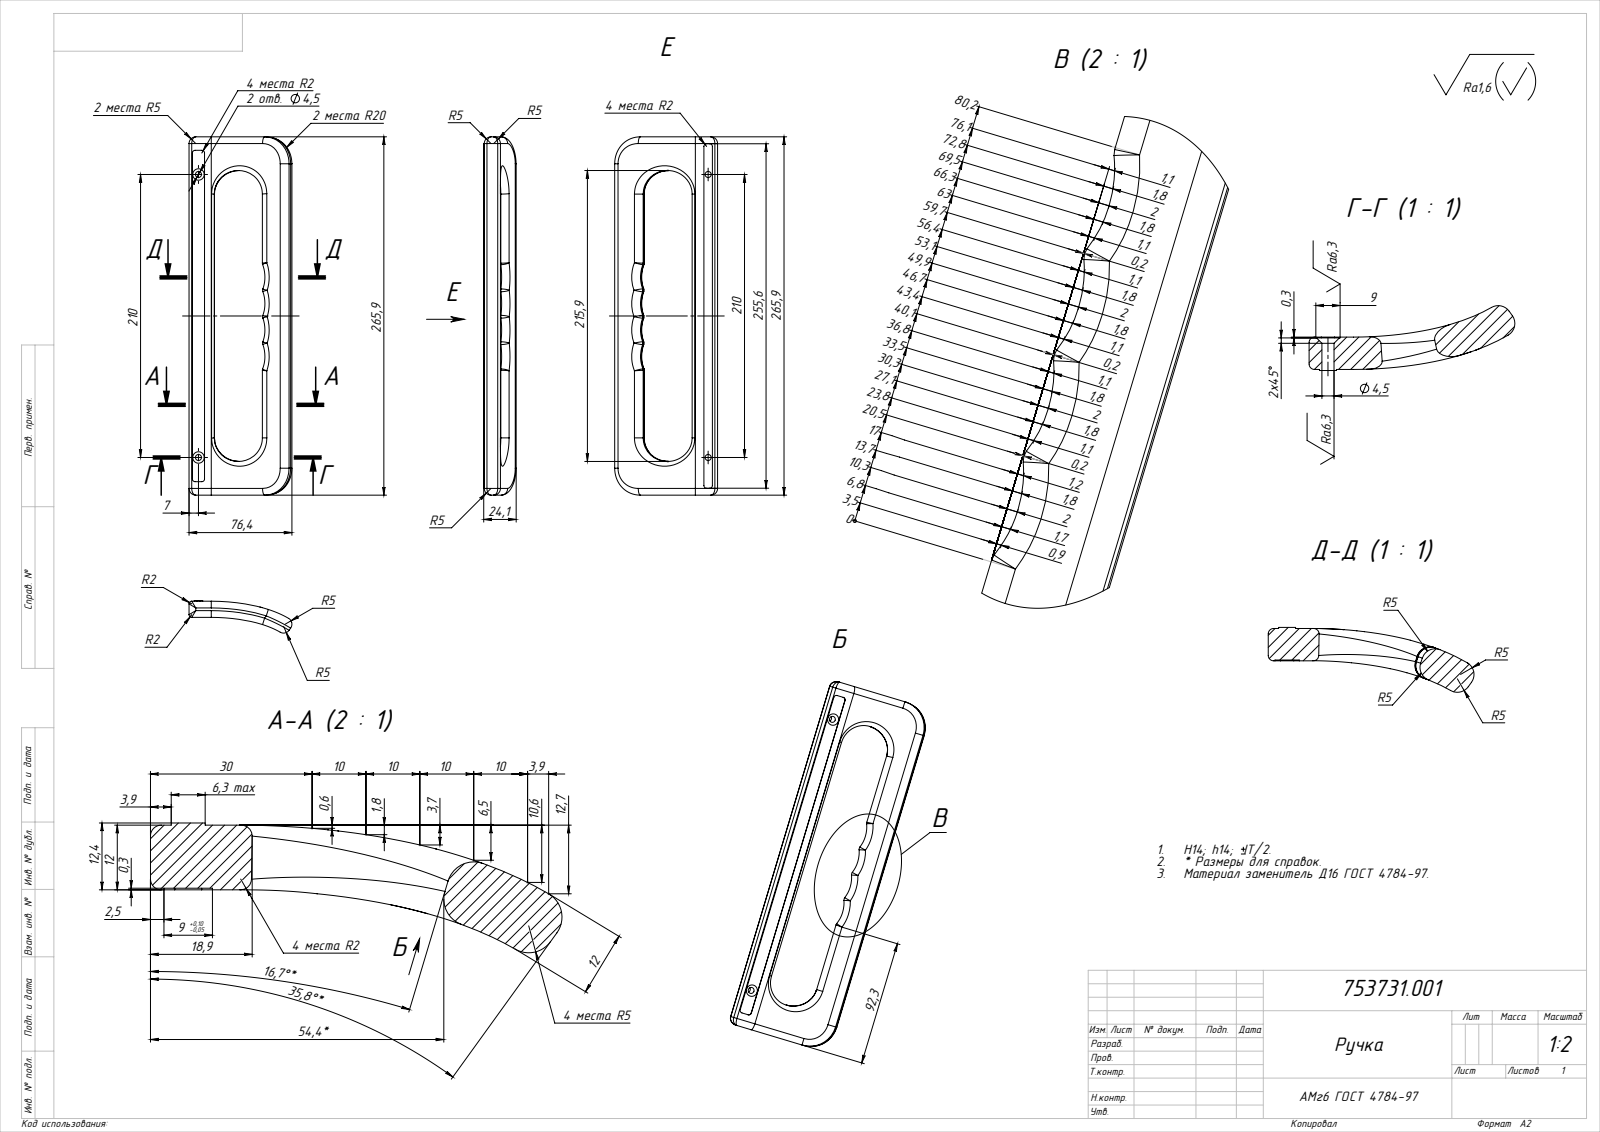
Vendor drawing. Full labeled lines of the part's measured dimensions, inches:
Part name (STEP PRODUCT): ПТРВ.753731.001 Ручка изм.1 04.02.21
STEP written by: SolidWorks 2018 (AUTOMOTIVE_DESIGN)
Units: inches
Bodies: 1 solid, 110 faces (19 planar, 28 cylindrical, 63 other)
Overall size (bounding box): 10.469 × 3.007 × 0.948
Volume: 8.823 in³ · Surface area: 56.07 in²
Round holes (diameter × count): ⌀0.177 ×2, ⌀0.335 ×2
Partial cylindrical surfaces — rounded edges, fillets, slot ends (radius × count): R0.079 ×10, R0.197 ×8, R0.787 ×2
Main face-to-face distances: 0.461, 0.016, 0.476, 0.488, 0.472, 0.053, 0.301, 10.469, 0.4, 0.152
Hole centre spacings: 8.268
